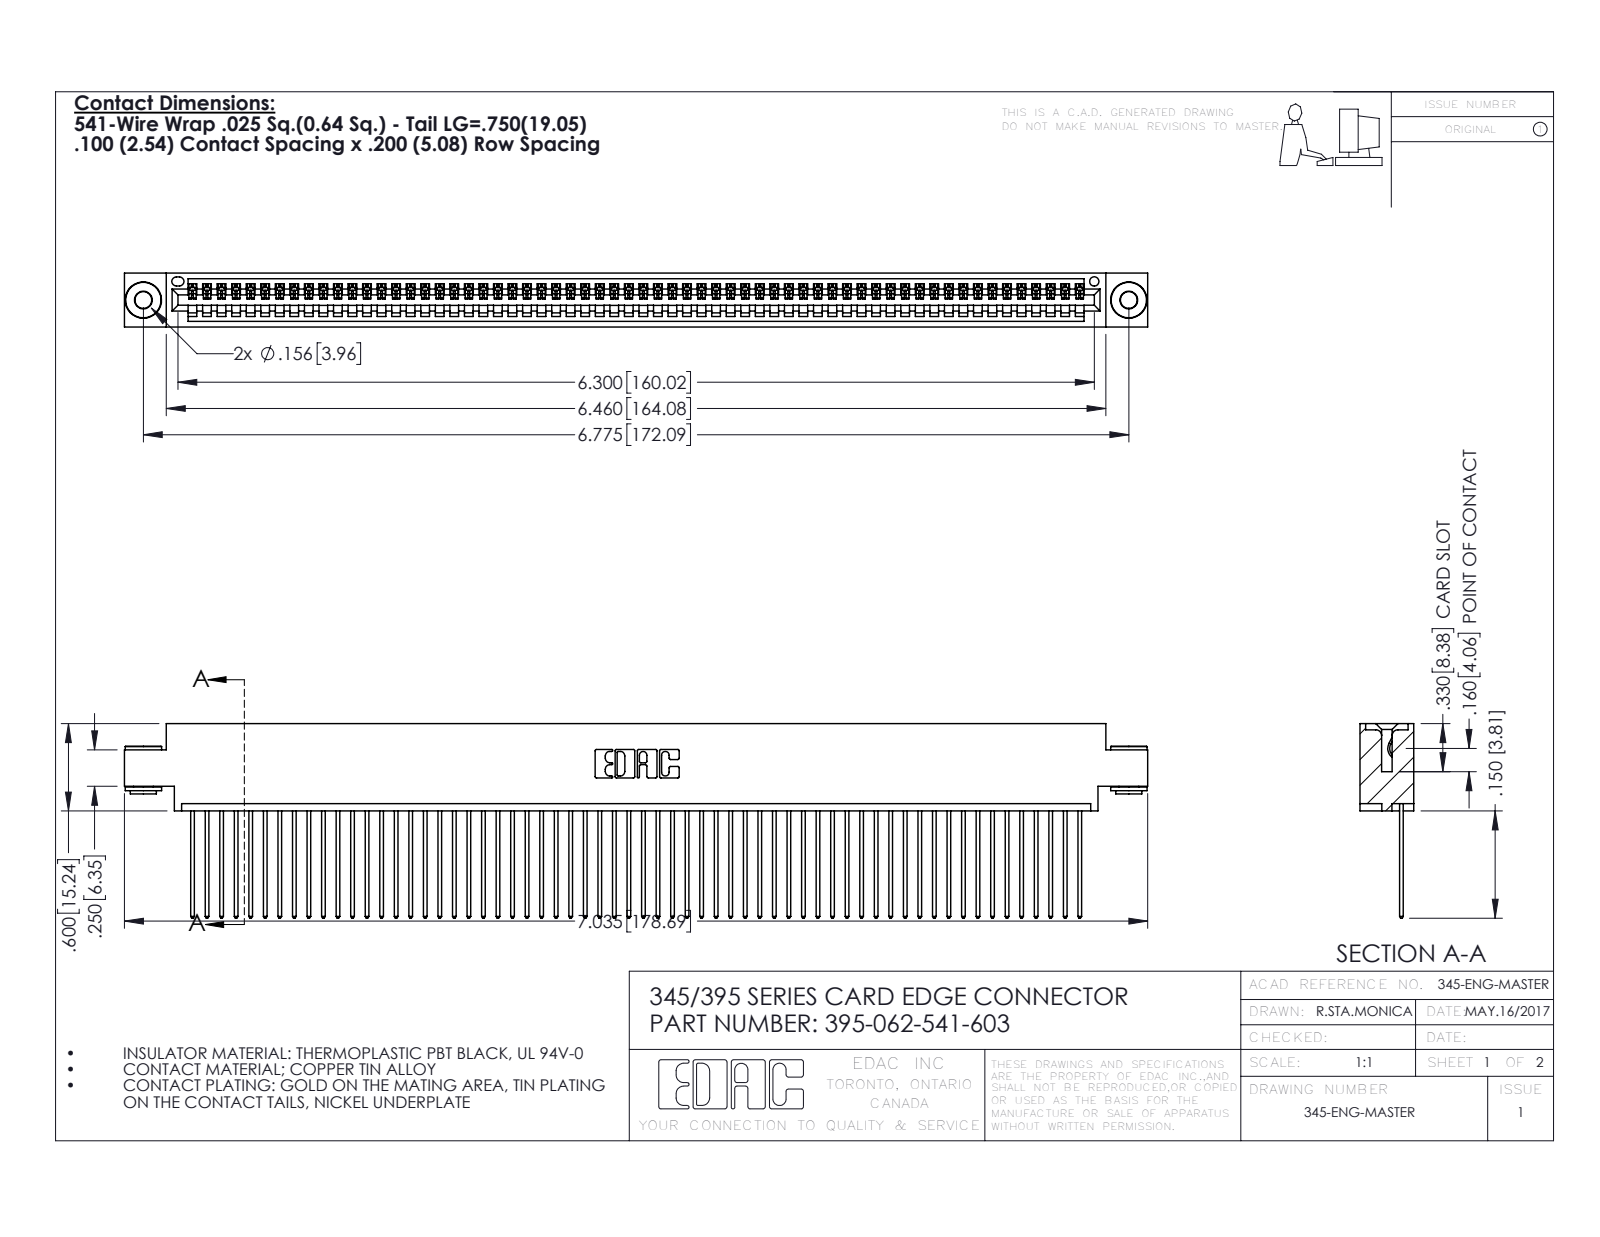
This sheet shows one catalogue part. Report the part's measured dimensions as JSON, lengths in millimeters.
{"part_name": "345 Part_0.170 Offset - 0.156 Dia-TH; 345-250-002_345-250-002-102; 345-292-001_345-293-141; 395-062-541-603", "step_written_by": "SolidWorks 2016 (CONFIG_CONTROL_DESIGN)", "units": "millimeters", "bodies": {"solids": 65, "faces": 3764, "planar": 2574, "cylindrical": 1182, "other": 8}, "overall_size": [178.7, 34, 9.4], "volume_mm3": 17240, "surface_area_mm2": 24740, "round_holes": [[2.9, 2], [4, 2], [1.6, 1]], "round_bosses_or_shafts": [[6.4, 2], [4.6, 2], [3.5, 2]], "partial_cylinders_radius": [[0.2, 124], [0.3, 124], [0.3, 22], [0.2, 6], [0.8, 6], [0.7, 3], [0.8, 2], [1, 2]], "face_to_face_distances": [1.8, 7.6, 9.4, 2.5, 6.9, 0.6, 5.1, 5.7, 4.4, 3.8], "hole_center_spacings": [6.9, 166.1, 172.1]}
